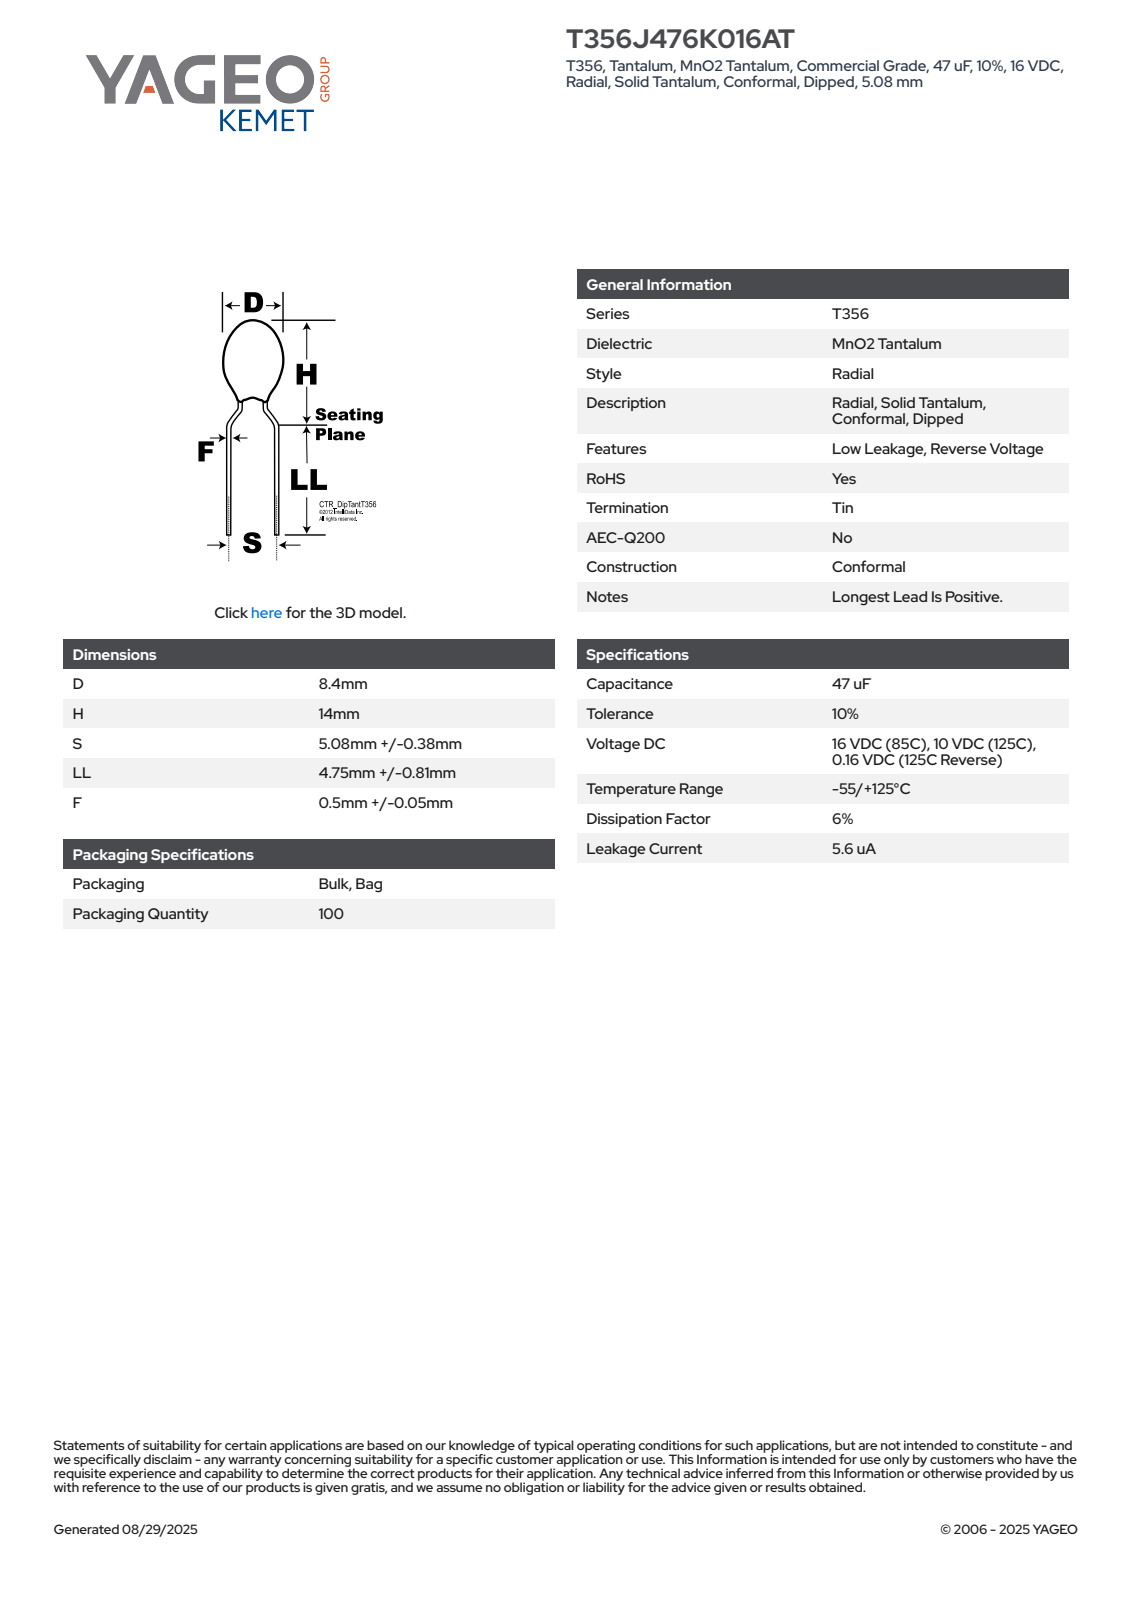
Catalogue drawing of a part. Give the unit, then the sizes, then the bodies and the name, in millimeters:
Units: millimetres
Overall size (bounding box): 19.56 × 8.4 × 8.4
Round bosses / shafts (diameter × count): ⌀0.55 ×6, ⌀8.4 ×1
Partial cylindrical surfaces — rounded edges, fillets, slot ends (radius × count): R4.19 ×1
Main face-to-face distances: 9.77, 9.79, 19.56, 16.2, 6.41, 3.36, 14.99, 5.2, 1.21, 4.57
Volume: 475 mm³ · Surface area: 341 mm²
Bodies: 1 solid, 96 faces (27 planar, 18 cylindrical, 51 other)
Part name (STEP PRODUCT): CTR_T356_D8.4H14S5.08LL5.56F0.55
STEP written by: SolidWorks 2014 (AUTOMOTIVE_DESIGN)
